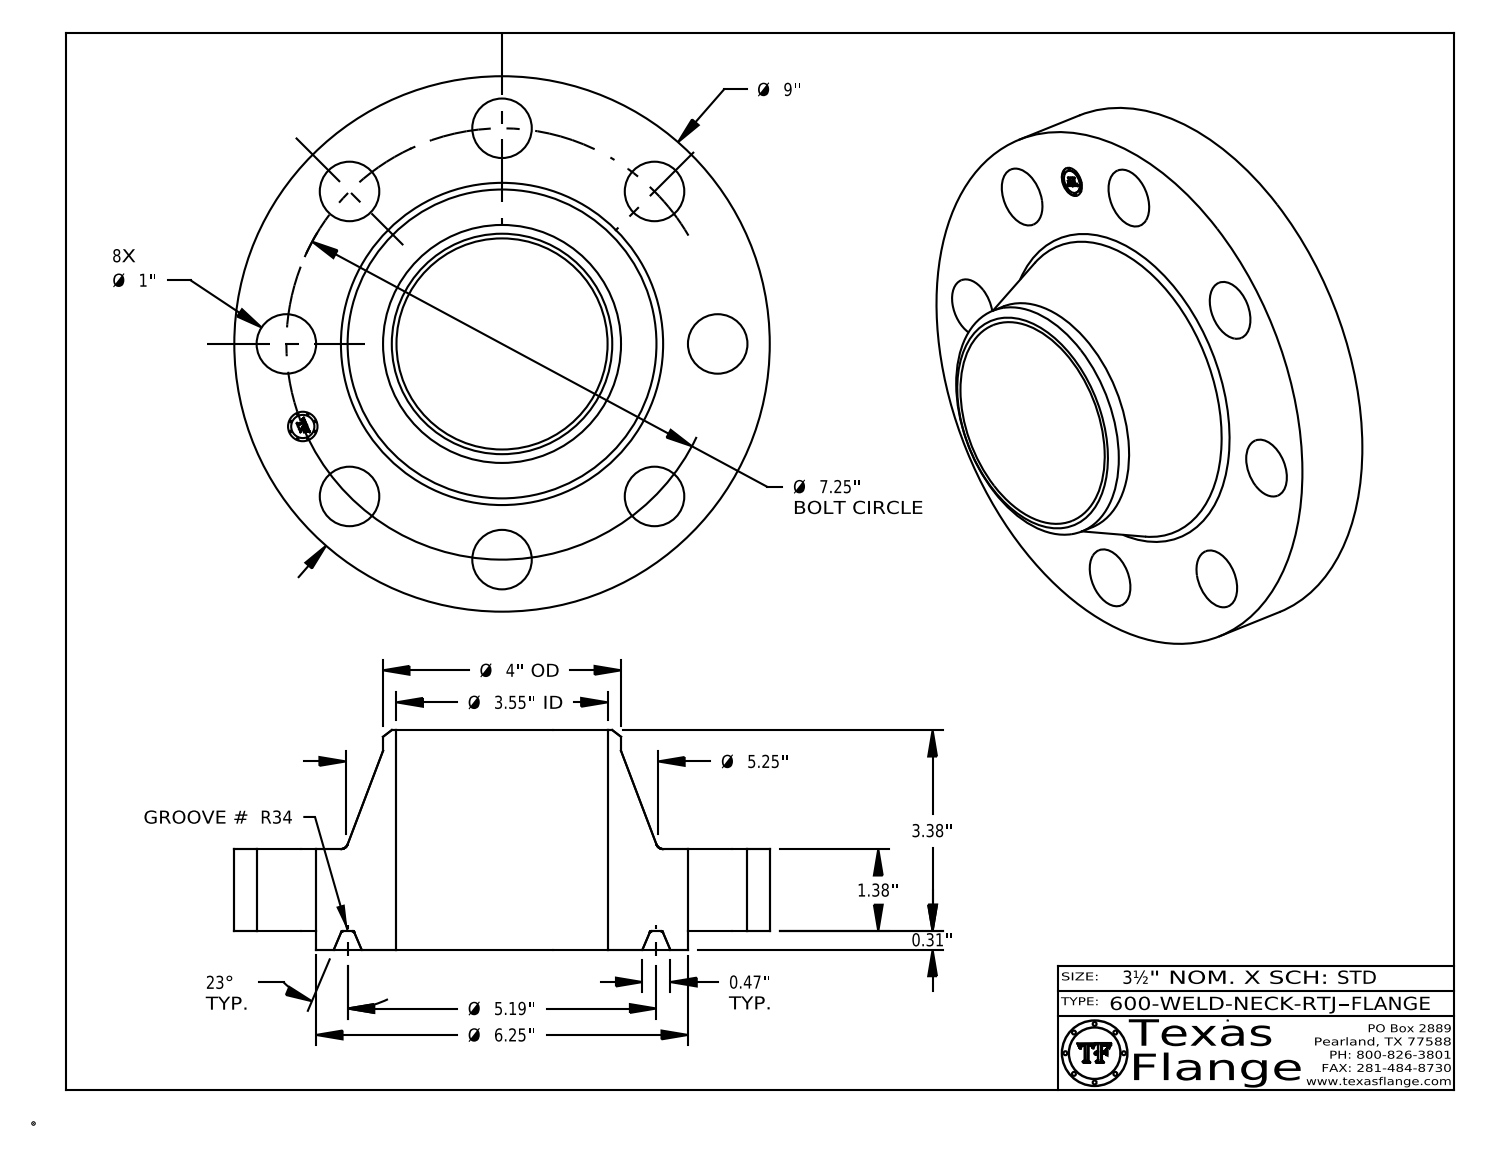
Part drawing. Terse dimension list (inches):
name: 600-WELD-NECK-RTJ
written by: CATIA V5 STEP AP214 (AUTOMOTIVE_DESIGN)
unit: in
bodies: 1 solid, 429 faces (371 planar, 44 cylindrical, 14 other)
size: 9 × 9 × 3.693
volume: 82.71 in³; area: 242.3 in²
holes: 8× ⌀1, 1× ⌀0.495, 1× ⌀3.548
bosses: 8× ⌀0.03, 1× ⌀9, 1× ⌀6.25, 1× ⌀4, 1× ⌀0.39
face distances: 1.38, 0.313, 1.693, 3.693, 3.38, 2, 1.678, 1.365, 0.015, 2.015
hole spacings: 3.625, 2.774, 5.127, 6.698, 7.25, 1.415, 7.111, 4.028
